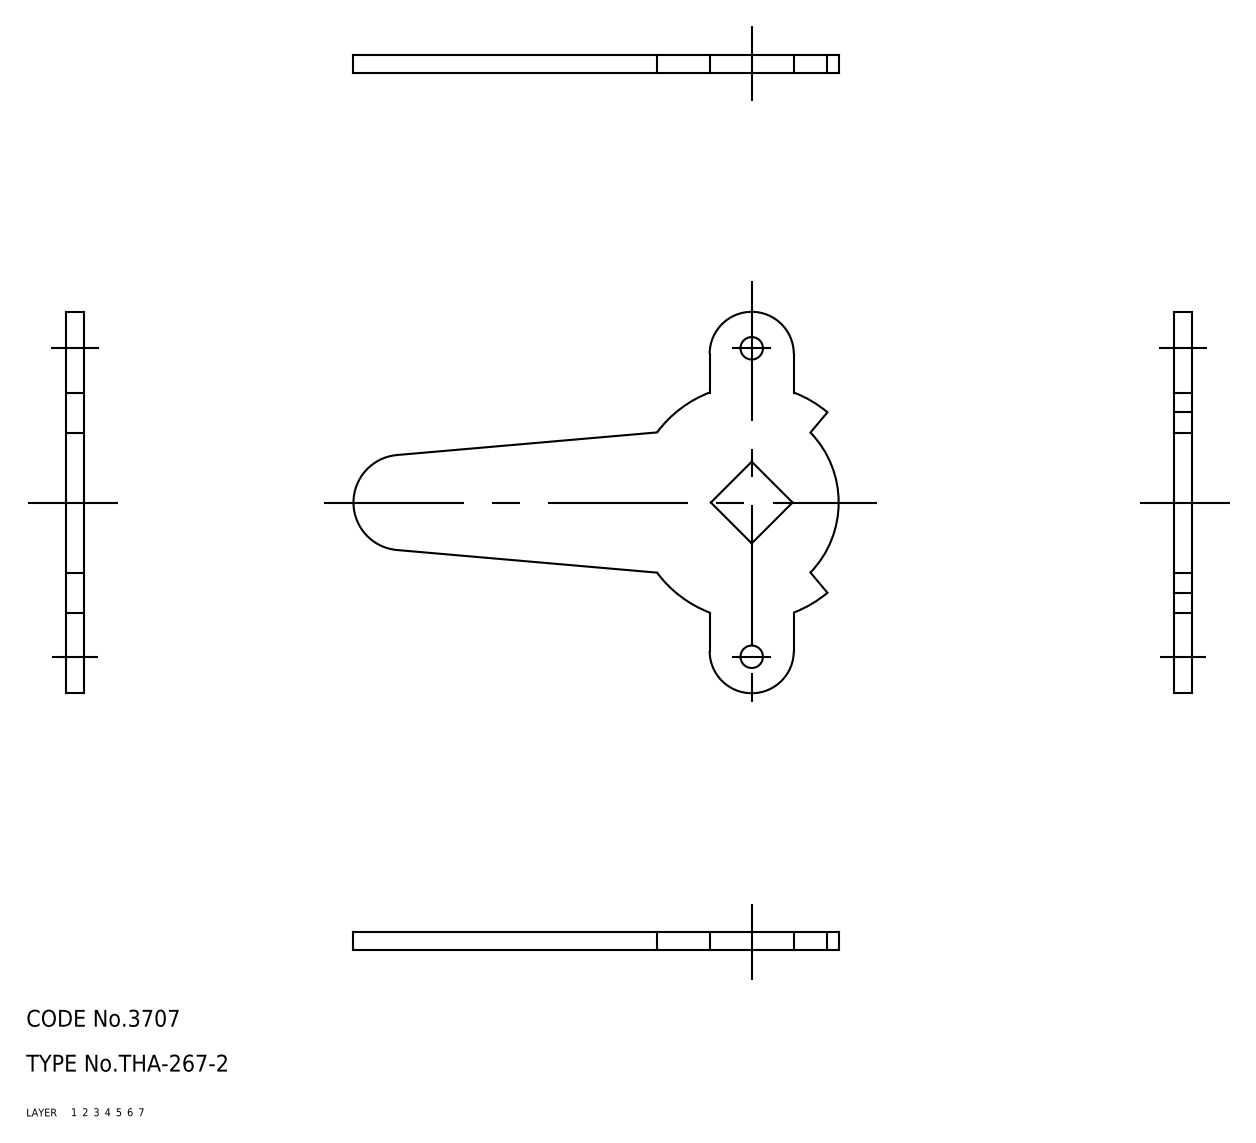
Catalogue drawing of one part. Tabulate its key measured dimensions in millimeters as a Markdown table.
| quantity | value |
| --- | --- |
| part name | cam |
| STEP written by | CADfix (AUTOMOTIVE_DESIGN) |
| units | millimeters |
| bodies | 1 solid, 26 faces (0 planar, 0 cylindrical, 26 other) |
| overall size | 86.5 × 68 × 3.2 |
| volume | 7 823 mm³ |
| surface area | 5 959 mm² |
